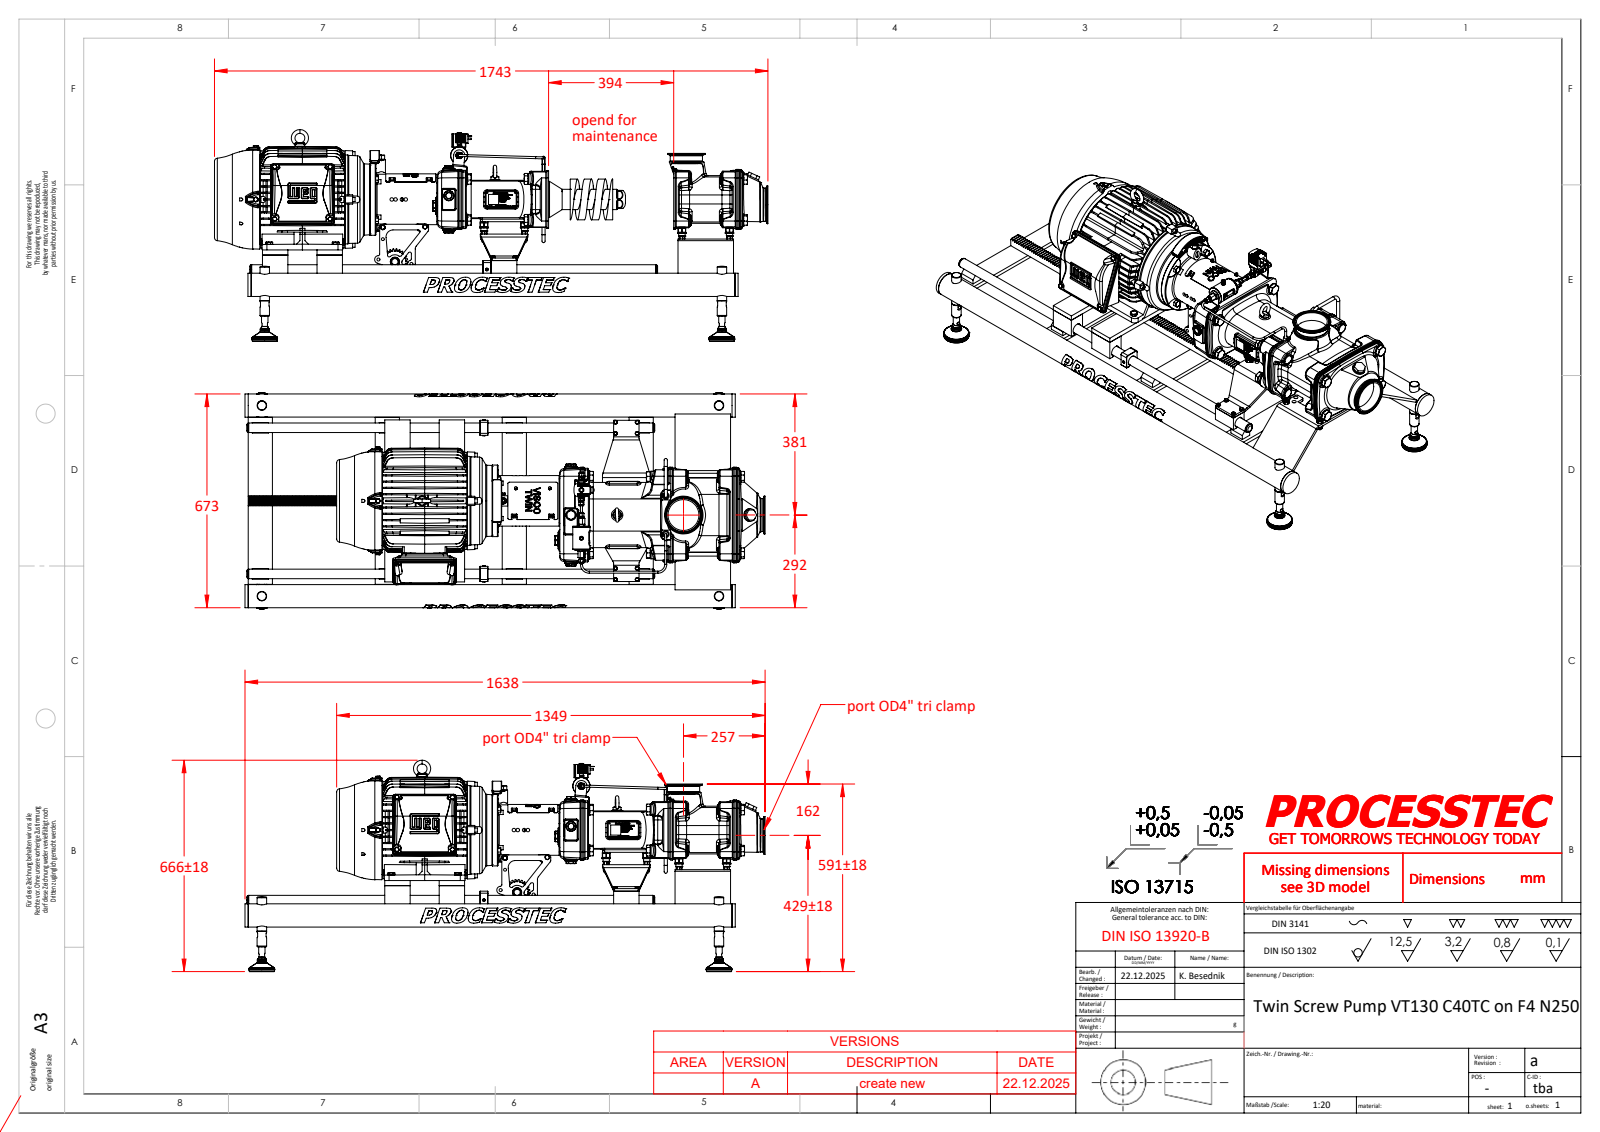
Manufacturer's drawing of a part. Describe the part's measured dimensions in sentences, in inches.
The part is named "001017; 001473; Teil4^001381; VT130-N250-000932 (+8 more)". Its 3-D file was written by "SolidWorks 2023 (AUTOMOTIVE_DESIGN)". It is 200 solids with 18383 faces: 7169 planar, 3569 cylindrical and 7645 other. Overall it measures 64.488 by 26.791 by 26.211 inches. Its volume is 4 311 cubic inches and its surface area 10 950 square inches. Round holes: 20 of diameter 0.197, 20 of diameter 0.335, 13 of diameter 0.512, 13 of diameter 0.689, 12 of diameter 0.433, 11 of diameter 0.161, 11 of diameter 0.268, 9 of diameter 0.315, 9 of diameter 0.402, 9 of diameter 0.413, 8 of diameter 0.252, 8 of diameter 0.398. Round bosses or shafts: 35 of diameter 0.394, 21 of diameter 0.236, 16 of diameter 0.787, 14 of diameter 0.472, 12 of diameter 0.945, 12 of diameter 0.591, 12 of diameter 0.315, 11 of diameter 0.669. Partial cylindrical surfaces (rounded edges, fillets, slot ends): 221 of radius 0.118, 82 of radius 0.059, 50 of radius 0.019, 49 of radius 0.236, 30 of radius 0.197, 29 of radius 0.079, 28 of radius 0.157, 27 of radius 0.047. The main face-to-face distances are 0.78, 0.315, 0.5, 1.559, 10.469, 0.551, 0.228, 4.772, 24.774, 14.305. The hole center spacings are 18.166, 15.748, 5.091, 9.055, 32.772, 2.165, 24, 31.496.
